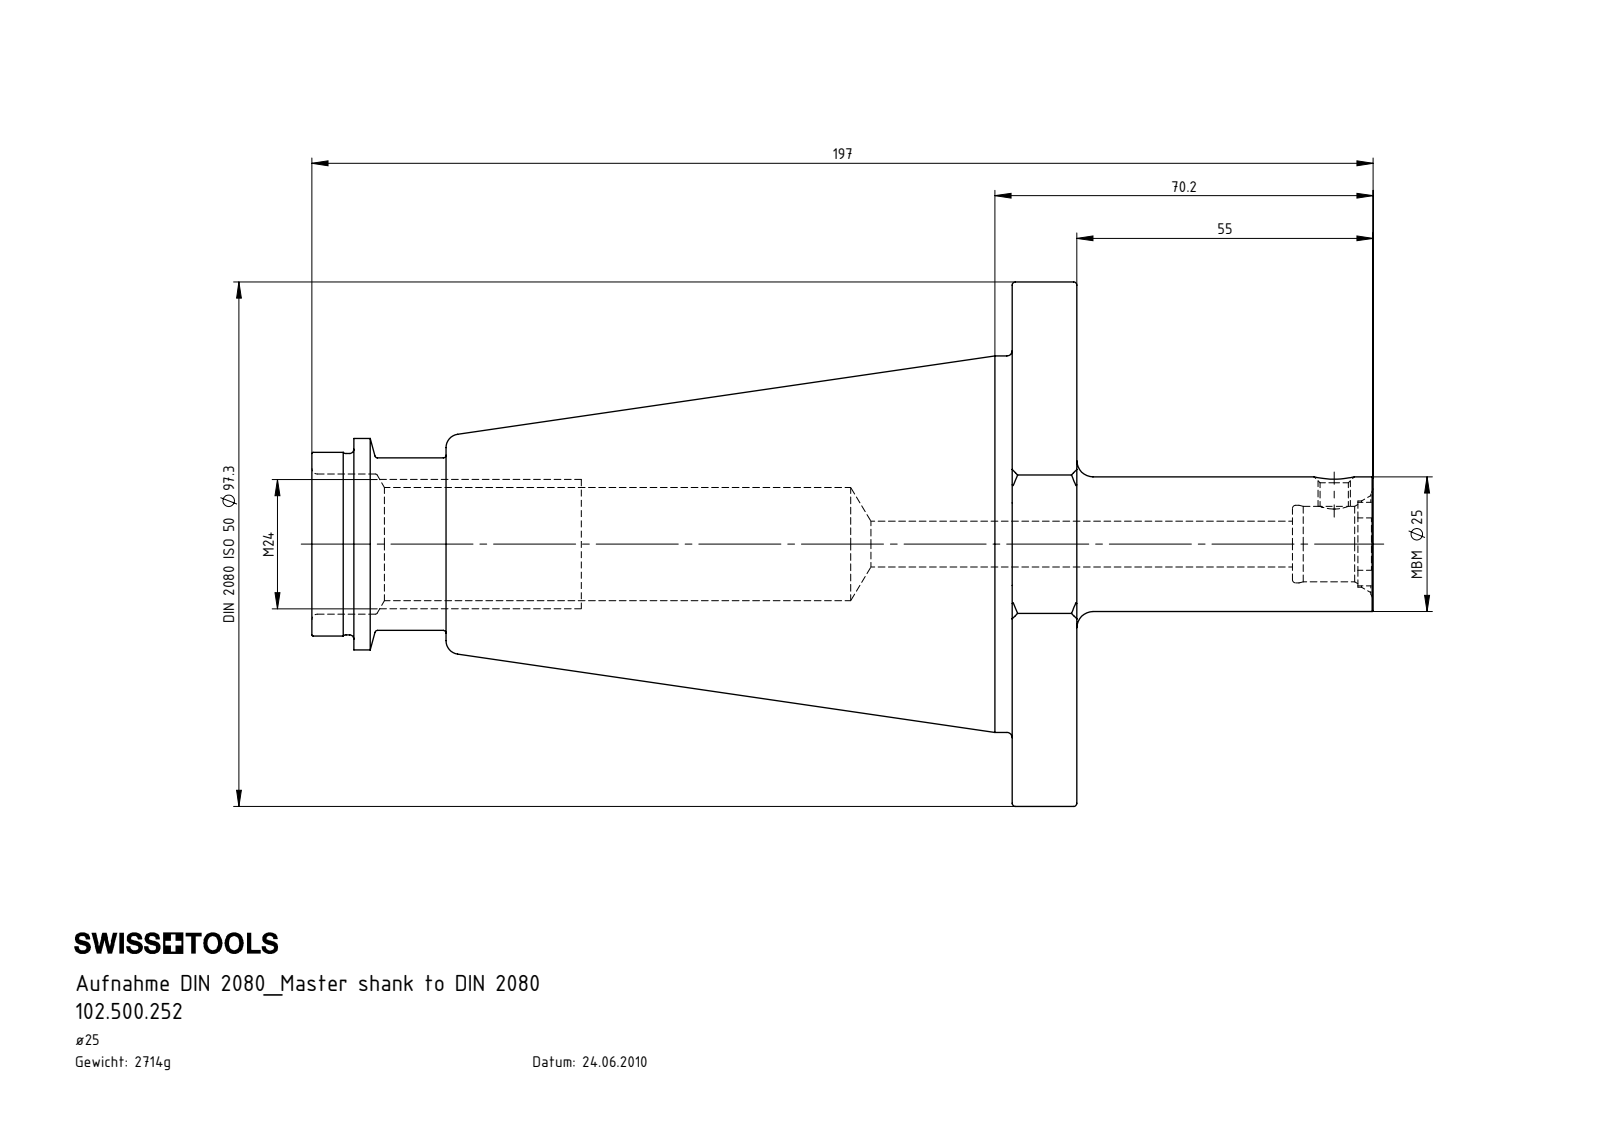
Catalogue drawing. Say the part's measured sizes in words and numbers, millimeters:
The part is named "102.500.252". Its 3-D file was written by "SolidWorks 2017 (CONFIG_CONTROL_DESIGN)". It is 1 solid with 128 faces: 31 planar, 49 cylindrical and 48 other. Overall it measures 167 by 97.3 by 93.84 millimeters. Its volume is 332 738 cubic millimeters and its surface area 47 079 square millimeters. Round holes: 1 of diameter 5.25, 1 of diameter 8.5, 1 of diameter 14, 1 of diameter 14.4, 1 of diameter 21, 1 of diameter 26. Round bosses or shafts: 1 of diameter 97.3, 1 of diameter 69.85, 1 of diameter 39.24, 1 of diameter 34.05, 1 of diameter 33.65, 1 of diameter 32, 1 of diameter 25. Partial cylindrical surfaces (rounded edges, fillets, slot ends): 12 of radius 2, 4 of radius 2.7, 1 of radius 8, 1 of radius 9.53. The main face-to-face distances are 12, 130, 142, 70.2, 7.8, 122.2, 134.2, 25.7, 24.9, 17.1.
